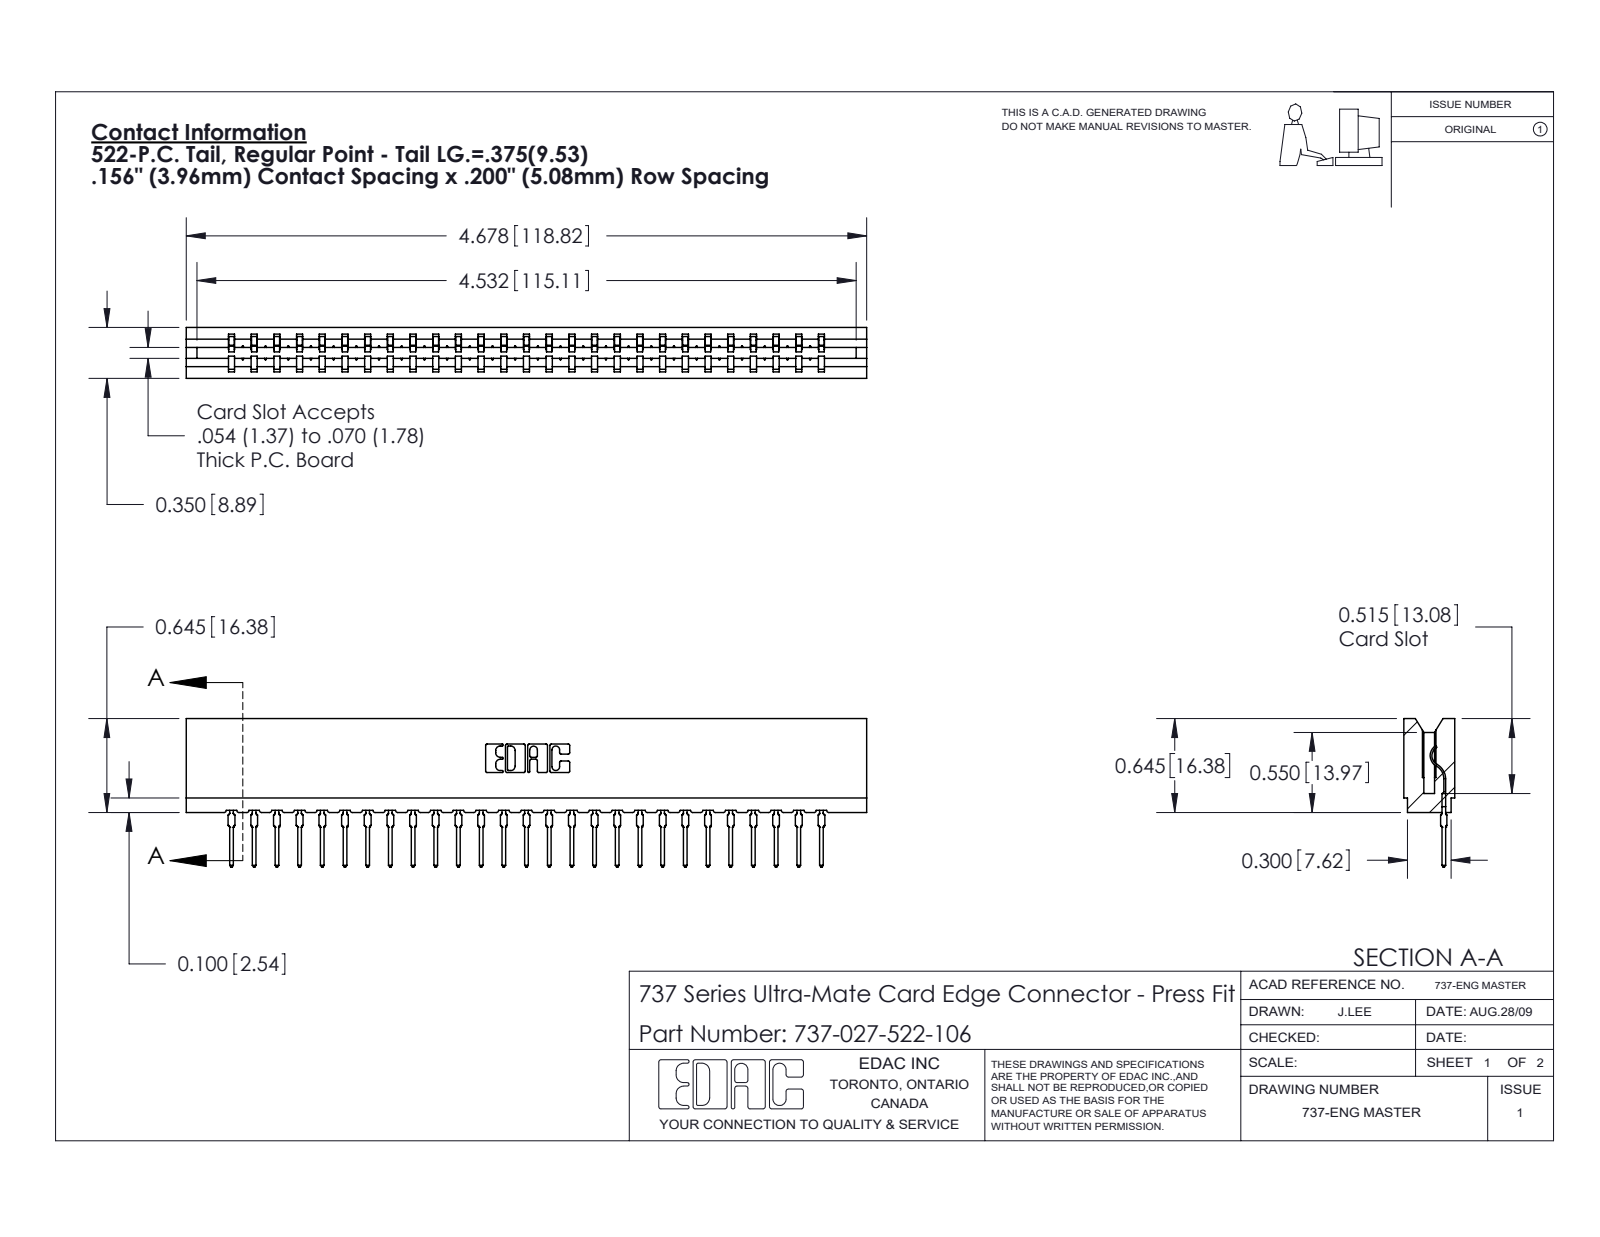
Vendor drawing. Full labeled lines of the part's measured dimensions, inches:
Part name (STEP PRODUCT): 745-292-001_522; 737 Part_Insulator Option - 06; 737-027-522-106
STEP written by: SolidWorks 2020 (CONFIG_CONTROL_DESIGN)
Units: inches
Bodies: 28 solids, 3146 faces (1891 planar, 553 cylindrical, 702 other)
Overall size (bounding box): 4.678 × 1.021 × 0.35
Volume: 0.707 in³ · Surface area: 23.81 in²
Partial cylindrical surfaces — rounded edges, fillets, slot ends (radius × count): R0.015 ×54, R0.021 ×54, R0.01 ×22, R0.007 ×6, R0.031 ×6, R0.005 ×4, R0.011 ×4, R0.026 ×3
Main face-to-face distances: 0.138, 0.212, 0.35, 0.074, 0.156, 0.624, 0.045, 0.305, 0.093, 0.167
